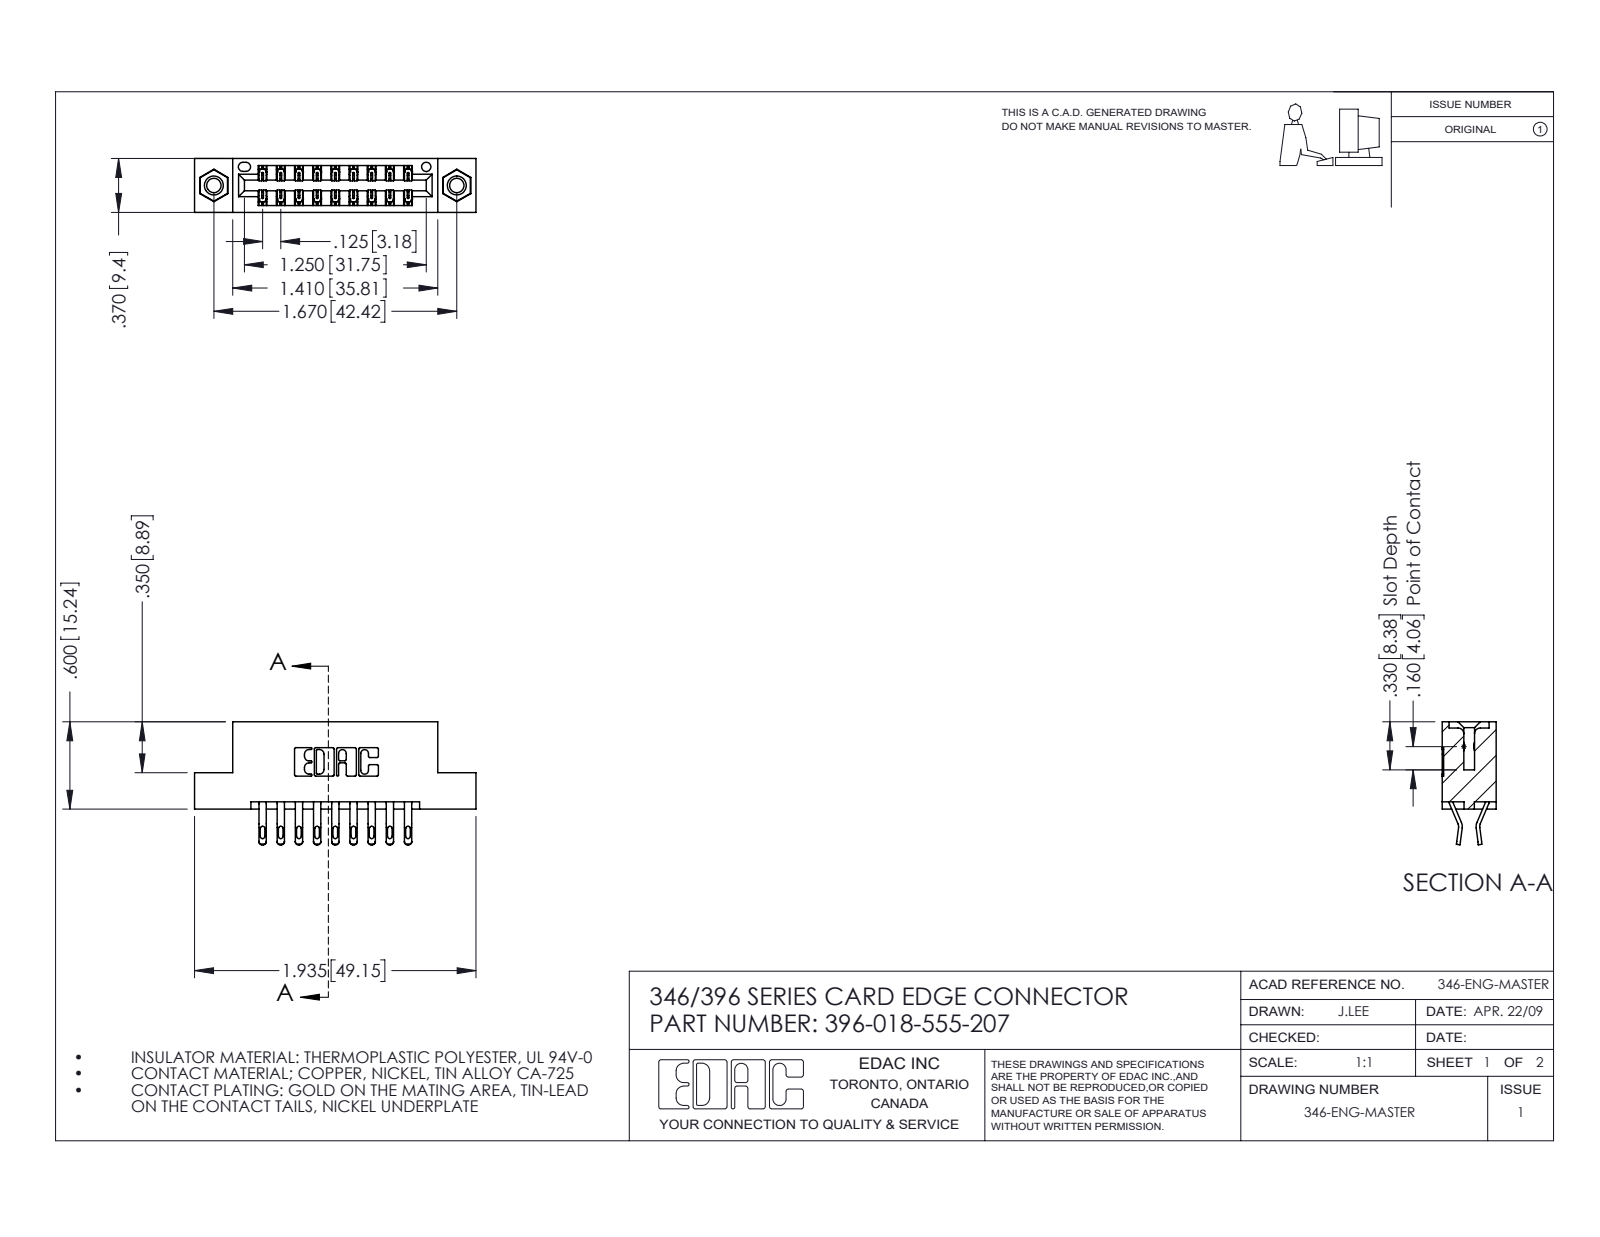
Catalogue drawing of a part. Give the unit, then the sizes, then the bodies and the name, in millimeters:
Units: millimetres
Overall size (bounding box): 49.1 × 21.5 × 9.4
Round holes (diameter × count): ⌀2.5 ×2, ⌀3.2 ×2, ⌀4 ×2, ⌀1.6 ×1
Round bosses / shafts (diameter × count): ⌀3.9 ×2
Partial cylindrical surfaces — rounded edges, fillets, slot ends (radius × count): R0.4 ×36, R0.5 ×36, R0.2 ×27, R0.3 ×22, R0.2 ×6, R0.8 ×6, R0.7 ×3, R0.3 ×2
Main face-to-face distances: 6.4, 1.2, 8.2, 9.4, 0.6, 1.8, 7.6, 3.8, 5.6, 2.5
Hole centre spacings: 6.2, 37.2, 42.4
Volume: 4 570 mm³ · Surface area: 5 990 mm²
Bodies: 21 solids, 1226 faces (702 planar, 508 cylindrical, 16 other)
Part name (STEP PRODUCT): 396-018-555-207; 346 Part_Flush Mounting Lugs - 0.156 Dia-TI; 345-250-001_345-250-005-103; 345-292-001_555 Tail
STEP written by: SolidWorks 2016 (CONFIG_CONTROL_DESIGN)
